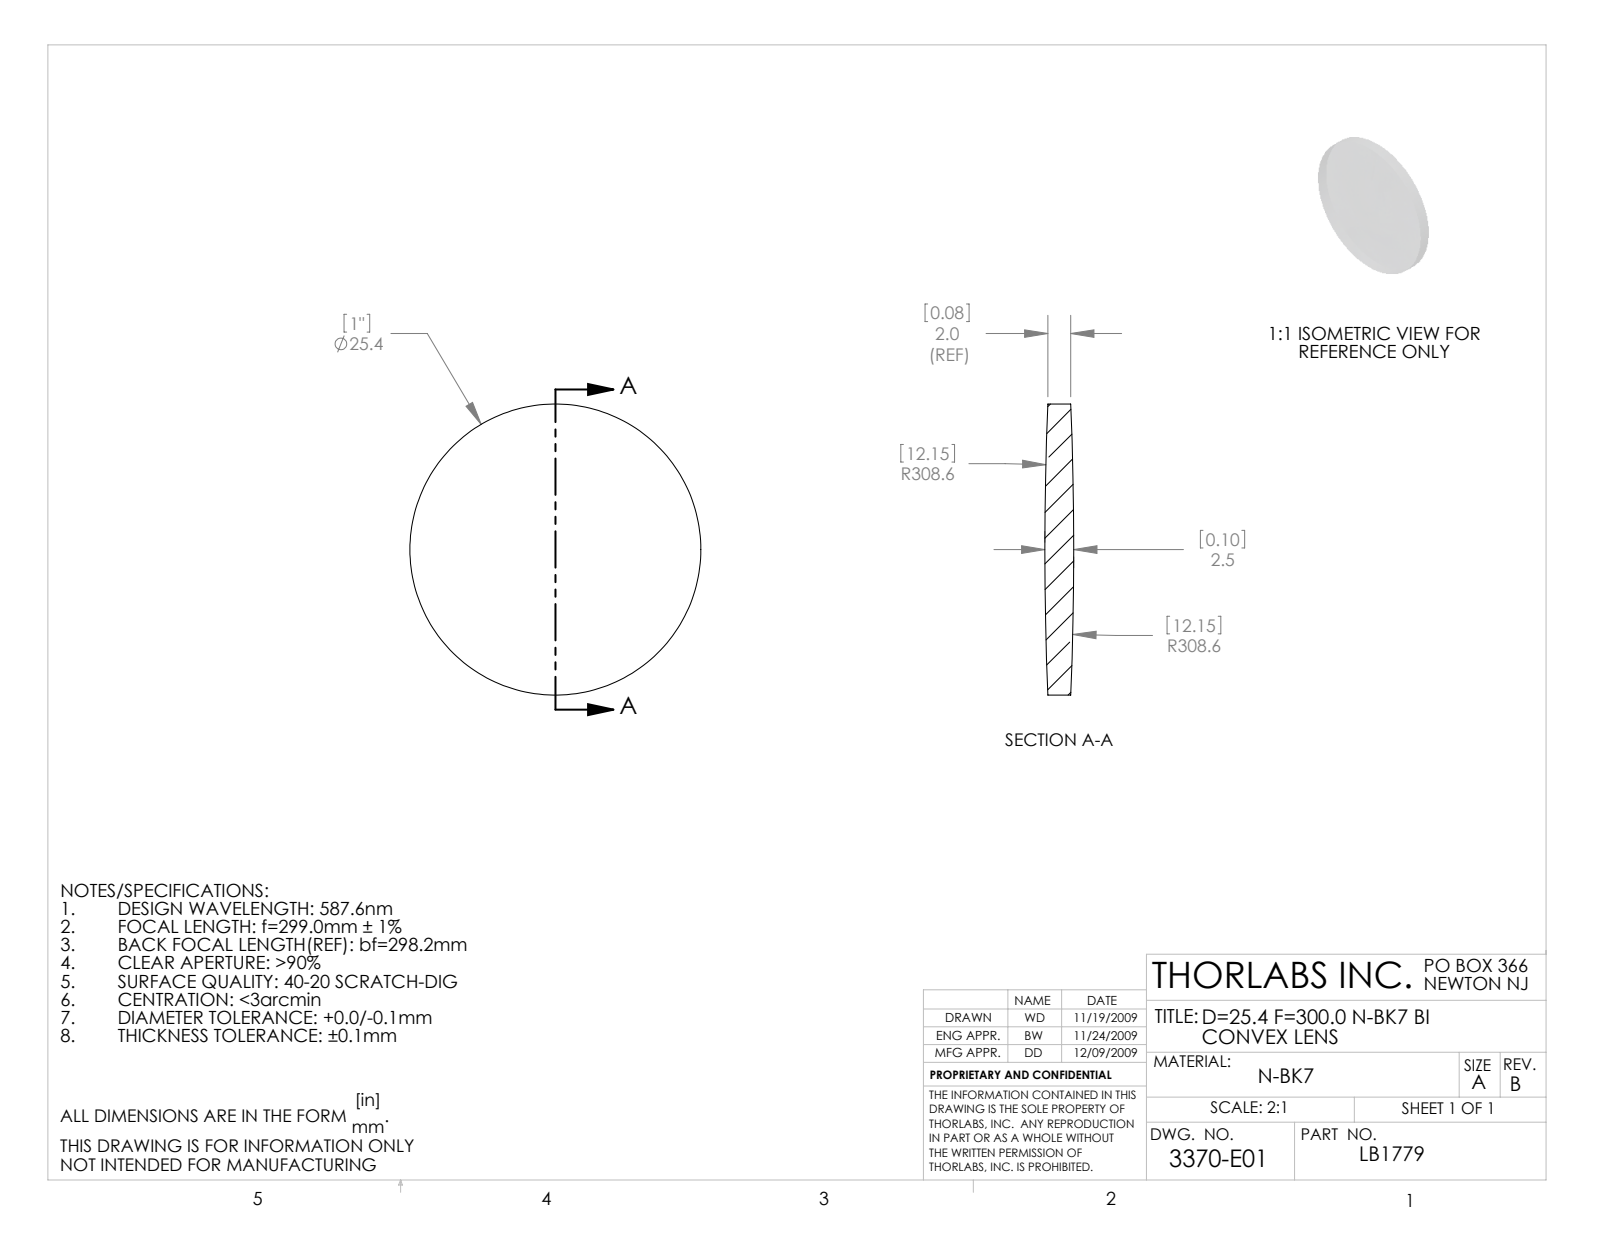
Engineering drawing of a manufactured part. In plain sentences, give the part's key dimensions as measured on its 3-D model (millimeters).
The part is named "3370-E0W". Its 3-D file was written by "SolidWorks 2009 (AUTOMOTIVE_DESIGN)". It is 1 solid with 6 faces: 0 planar, 2 cylindrical and 4 other. Overall it measures 25.4 by 25.4 by 2.52 millimeters. Its volume is 1 144 cubic millimeters and its surface area 1 173 square millimeters. Round bosses or shafts: 1 of diameter 25.4.
